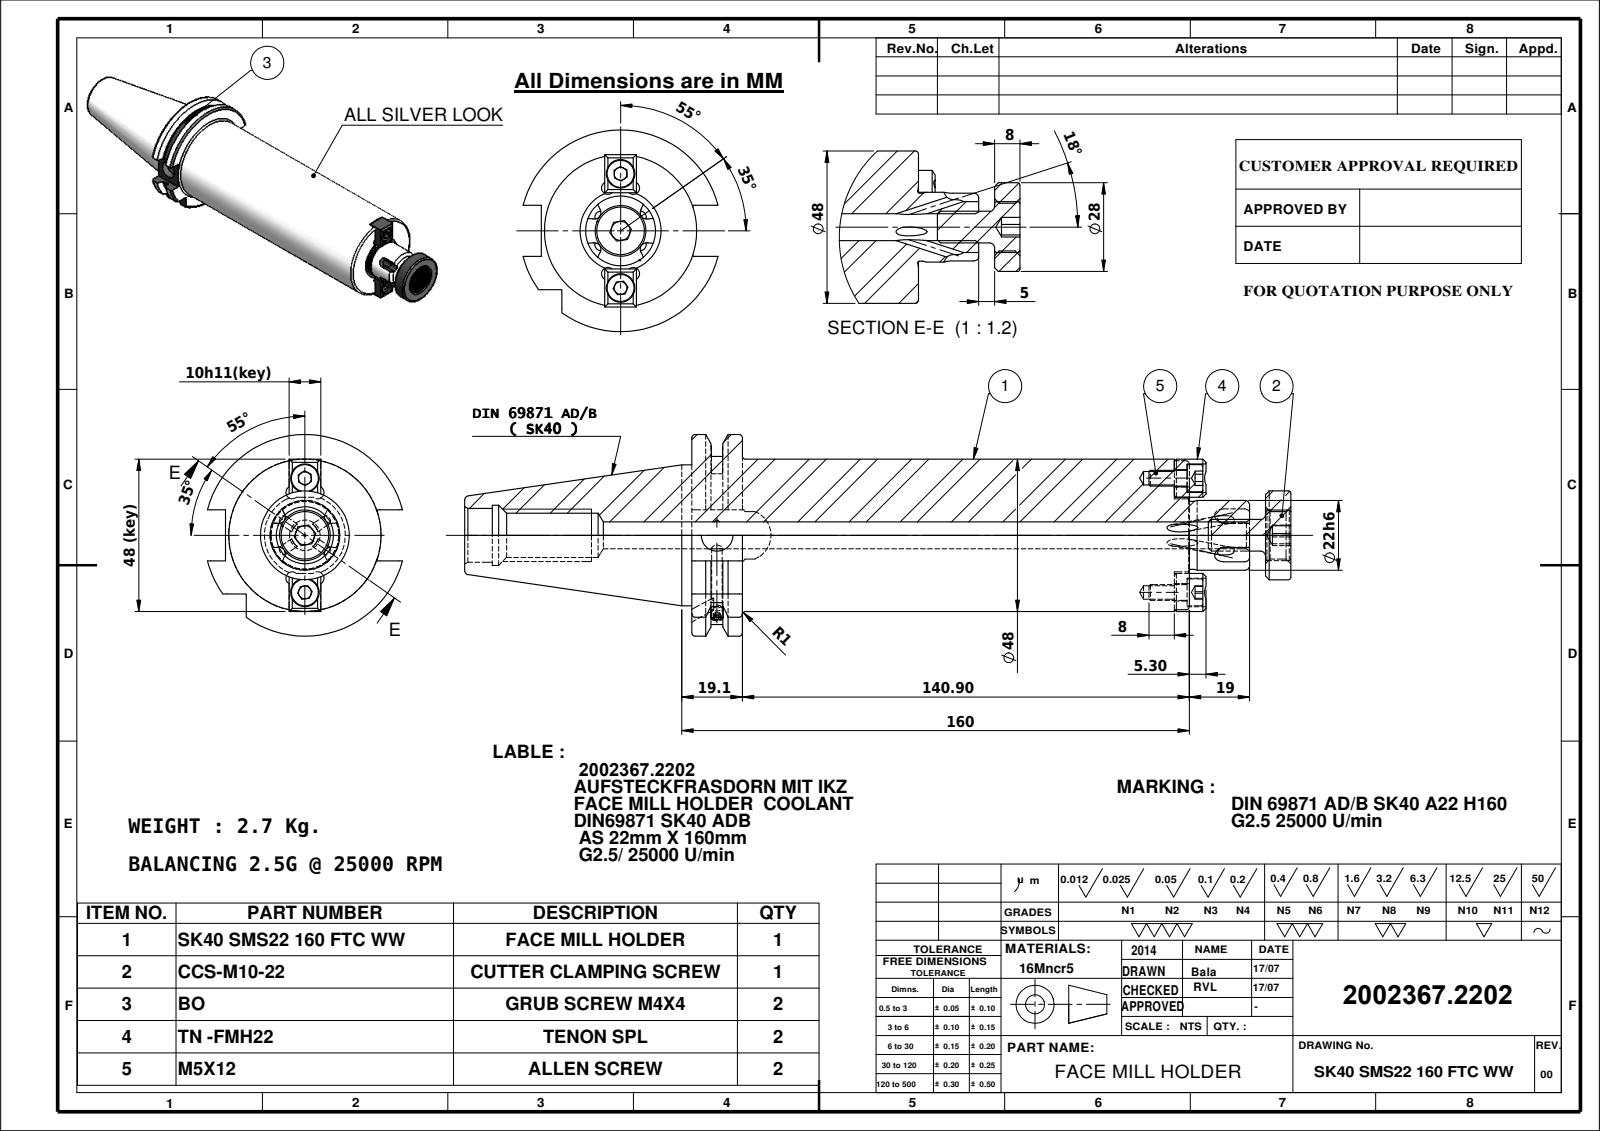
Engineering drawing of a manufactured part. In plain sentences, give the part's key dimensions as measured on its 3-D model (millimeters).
The part is named "SK40 SMS22 160 FTC WW; CCS-M10-22-1; CCS-M10-22; TN -FMH22 (+3 more)". Its 3-D file was written by "SolidWorks 2009 (CONFIG_CONTROL_DESIGN)". It is 9 solids with 343 faces: 142 planar, 90 cylindrical and 111 other. Overall it measures 260.4 by 63.55 by 61.48 millimeters. Its volume is 361 647 cubic millimeters and its surface area 54 262 square millimeters. Round holes: 4 of diameter 3, 2 of diameter 4.2, 2 of diameter 5.4, 2 of diameter 9, 1 of diameter 3.3, 1 of diameter 8.5, 1 of diameter 10, 1 of diameter 14, 1 of diameter 15, 1 of diameter 17, 1 of diameter 19. Round bosses or shafts: 2 of diameter 8.5, 2 of diameter 5, 2 of diameter 4, 1 of diameter 48, 1 of diameter 44.45, 1 of diameter 28, 1 of diameter 22, 1 of diameter 21.4. Partial cylindrical surfaces (rounded edges, fillets, slot ends): 8 of radius 2, 1 of radius 8.05, 1 of radius 28.12, 1 of radius 31.77. The main face-to-face distances are 156.8, 15.9, 140.9, 188.8, 172.9, 32, 24, 36.7, 152.1, 136.2. The hole center spacings are 18, 36.
